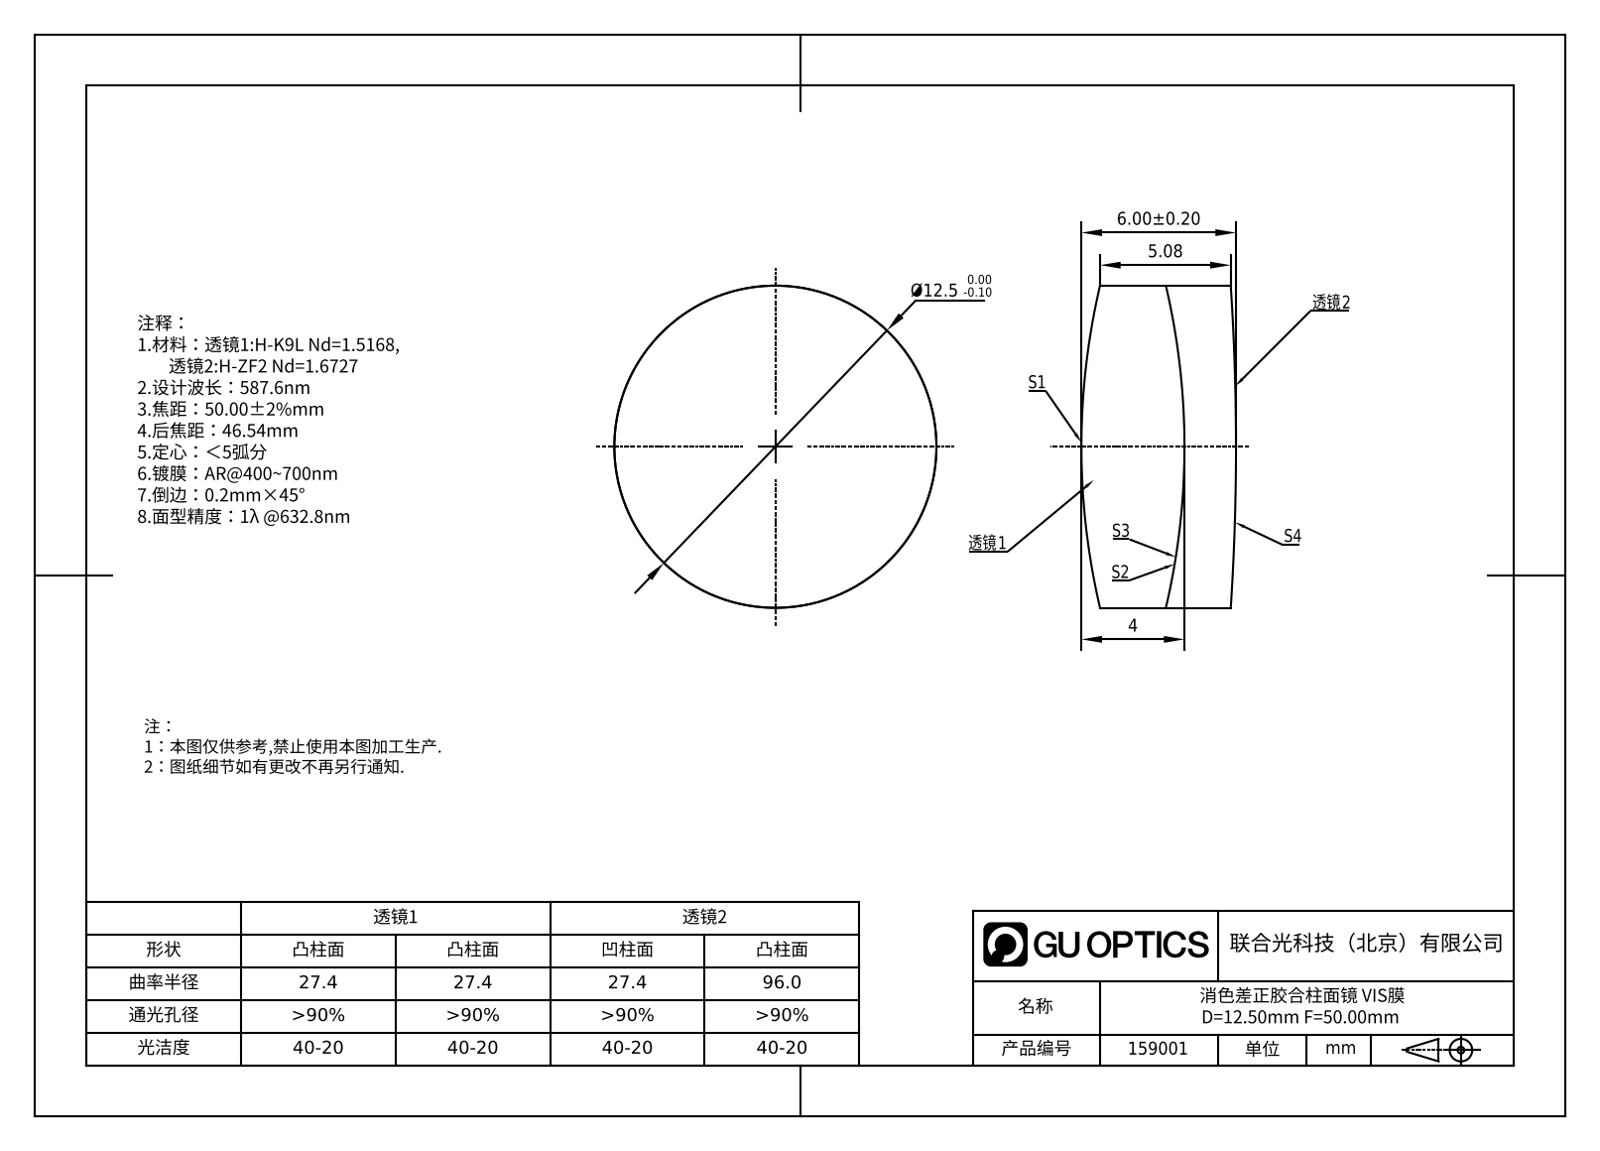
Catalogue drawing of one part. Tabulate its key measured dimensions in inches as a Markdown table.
| quantity | value |
| --- | --- |
| part name | 159001 |
| STEP written by | SolidWorks 2020 (CONFIG_CONTROL_DESIGN) |
| units | inches |
| bodies | 1 solid, 5 faces (0 planar, 5 cylindrical, 0 other) |
| overall size | 0.492 × 0.492 × 0.236 |
| volume | 0.043 in³ |
| surface area | 0.719 in² |
| round bosses / shafts (diameter × count) | 0.492 × 1 |
| partial cylindrical surfaces (radius × count) | 1.079 × 1, 3.78 × 1 |
